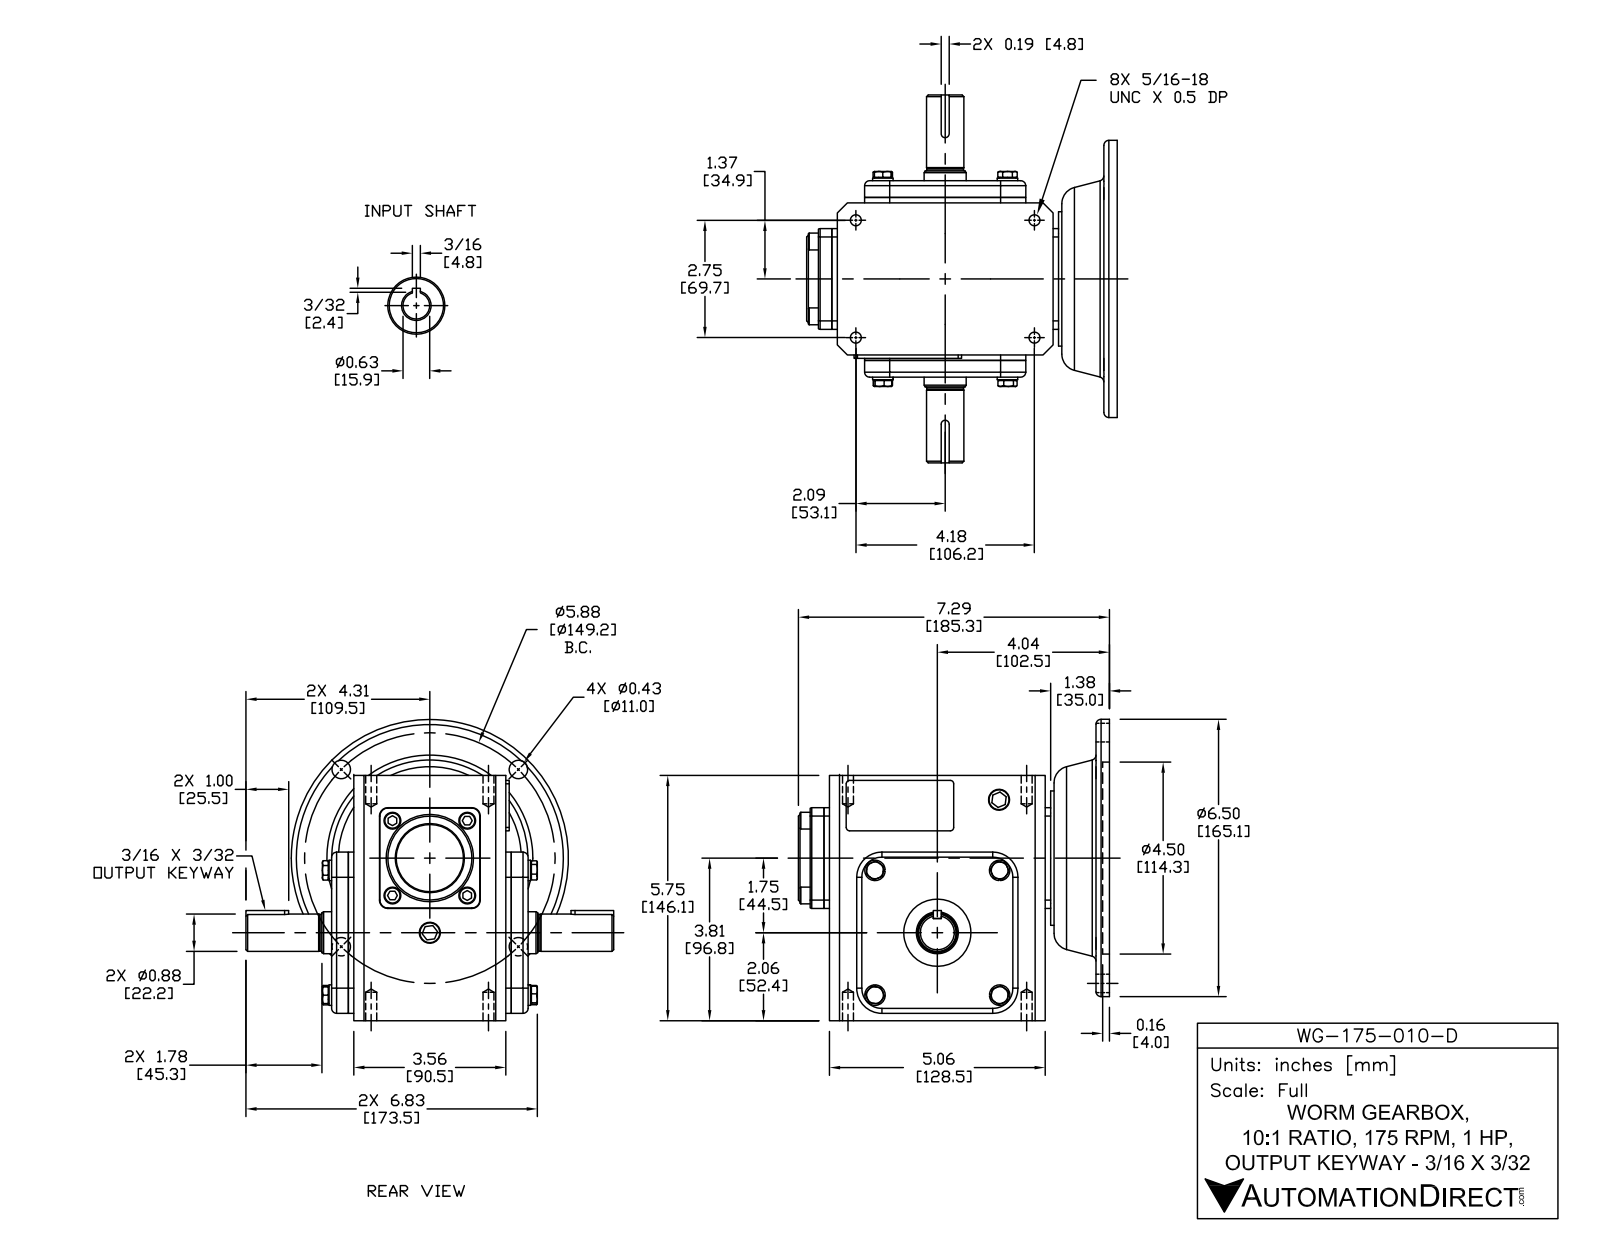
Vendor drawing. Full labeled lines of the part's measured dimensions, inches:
Part name (STEP PRODUCT): WG-175-010-D
STEP written by: SolidWorks 2015 (CONFIG_CONTROL_DESIGN)
Units: inches
Bodies: 45 solids, 647 faces (324 planar, 186 cylindrical, 137 other)
Overall size (bounding box): 8.622 × 7.283 × 7.06
Volume: 133.1 in³ · Surface area: 375.6 in²
Round holes (diameter × count): ⌀0.257 ×4, ⌀0.406 ×4, ⌀0.512 ×1, ⌀0.625 ×1, ⌀0.984 ×1, ⌀1.181 ×1, ⌀1.457 ×1, ⌀1.575 ×1, ⌀3.543 ×1, ⌀4.5 ×1
Round bosses / shafts (diameter × count): ⌀0.394 ×8, ⌀0.48 ×4, ⌀0.512 ×2, ⌀6.496 ×1, ⌀3.15 ×1, ⌀2.047 ×1, ⌀1.575 ×1, ⌀0.875 ×1
Partial cylindrical surfaces — rounded edges, fillets, slot ends (radius × count): R0.079 ×8, R0.118 ×8, R0.197 ×4, R0.591 ×4, R0.02 ×2, R0.039 ×2, R0.094 ×2
Main face-to-face distances: 0.128, 3.819, 4.213, 0.394, 4.085, 3.691, 0.522, 0.315, 5.75, 6.693
Hole centre spacings: 2.937, 4.154, 2.103, 2.75, 4.188, 4.354, 5.01, 5.875
